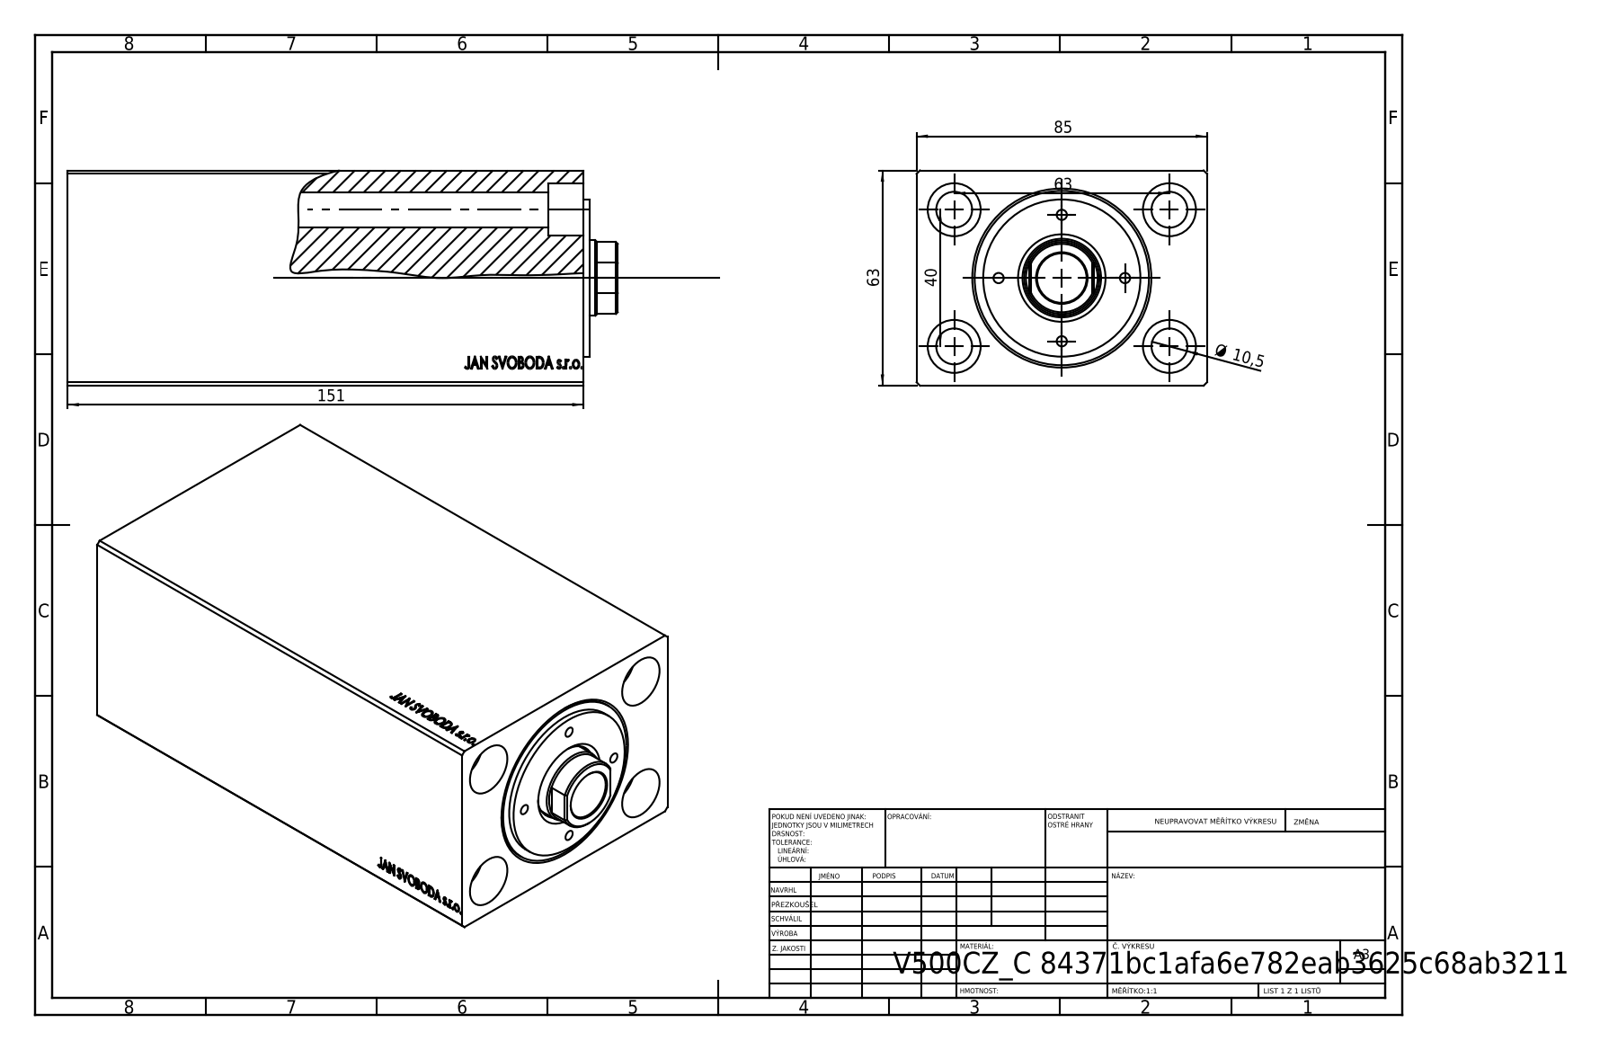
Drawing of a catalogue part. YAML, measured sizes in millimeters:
step_written_by: "SolidWorks 2019 (CONFIG_CONTROL_DESIGN)"
units: millimeters
bodies: {solids: 1, faces: 818, planar: 394, cylindrical: 42, other: 382}
overall_size: [151, 85, 63]
volume: 516011
surface_area: 96579
round_holes:
  - {diameter: 10.5, count: 4}
  - {diameter: 15.5, count: 4}
  - {diameter: 5.5, count: 2}
  - {diameter: 13.6, count: 2}
  - {diameter: 20, count: 2}
  - {diameter: 36, count: 1}
  - {diameter: 40, count: 1}
  - {diameter: 51, count: 1}
face_to_face_distances: [63, 85, 151, 136.3, 14.7, 150.8, 14.5, 10.33, 140.67, 80]
hole_center_spacings: [37.31, 40, 63, 74.63, 113]
